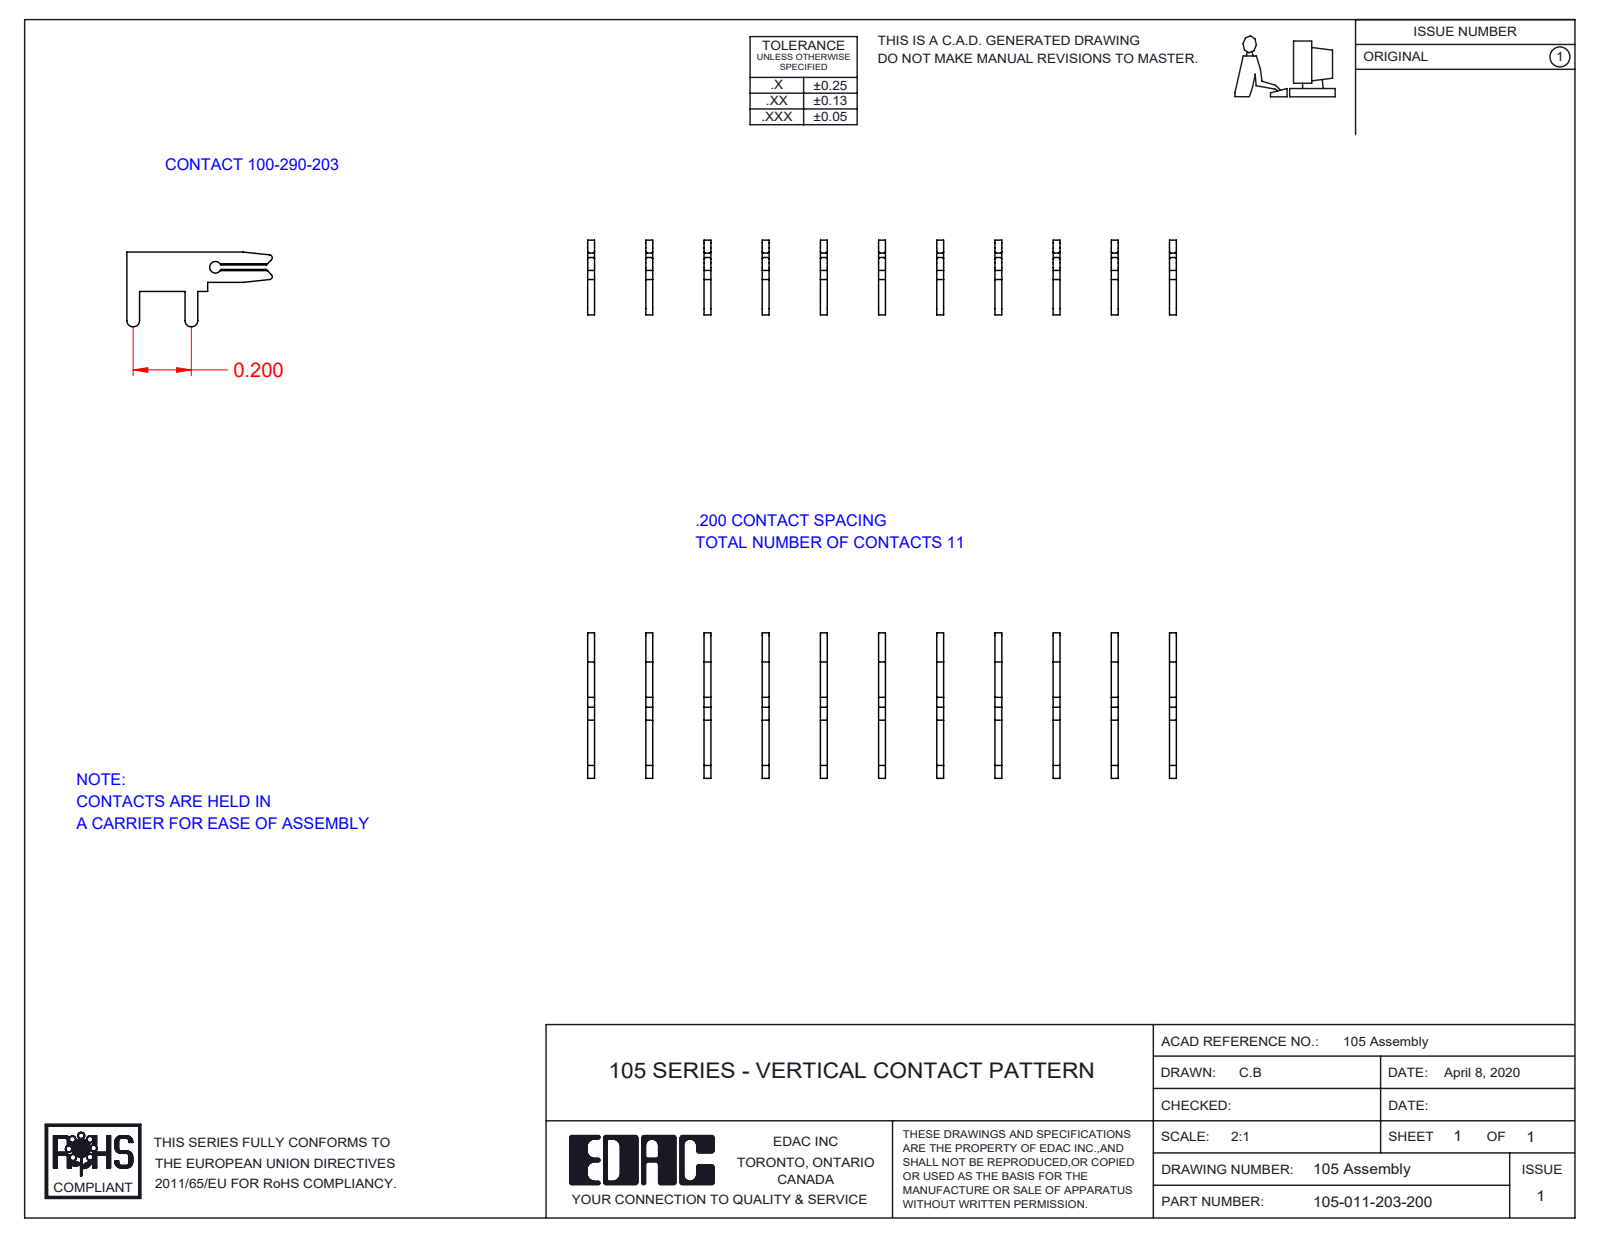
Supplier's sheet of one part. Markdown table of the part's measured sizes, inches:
| quantity | value |
| --- | --- |
| part name | 100-290-001_100-290-203; 105-011-203-200 |
| STEP written by | SolidWorks 2020 (CONFIG_CONTROL_DESIGN) |
| units | inches |
| bodies | 11 solids, 308 faces (231 planar, 77 cylindrical, 0 other) |
| overall size | 2.024 × 0.5 × 0.257 |
| volume | 0.017 in³ |
| surface area | 1.973 in² |
| round holes (diameter × count) | 0.04 × 1 |
| partial cylindrical surfaces (radius × count) | 0.01 × 2, 0.022 × 2 |
| main face-to-face distances | 0.2, 0.4, 0.6, 0.8, 1, 0.024, 0.224, 0.424, 1.2, 0.624 |
